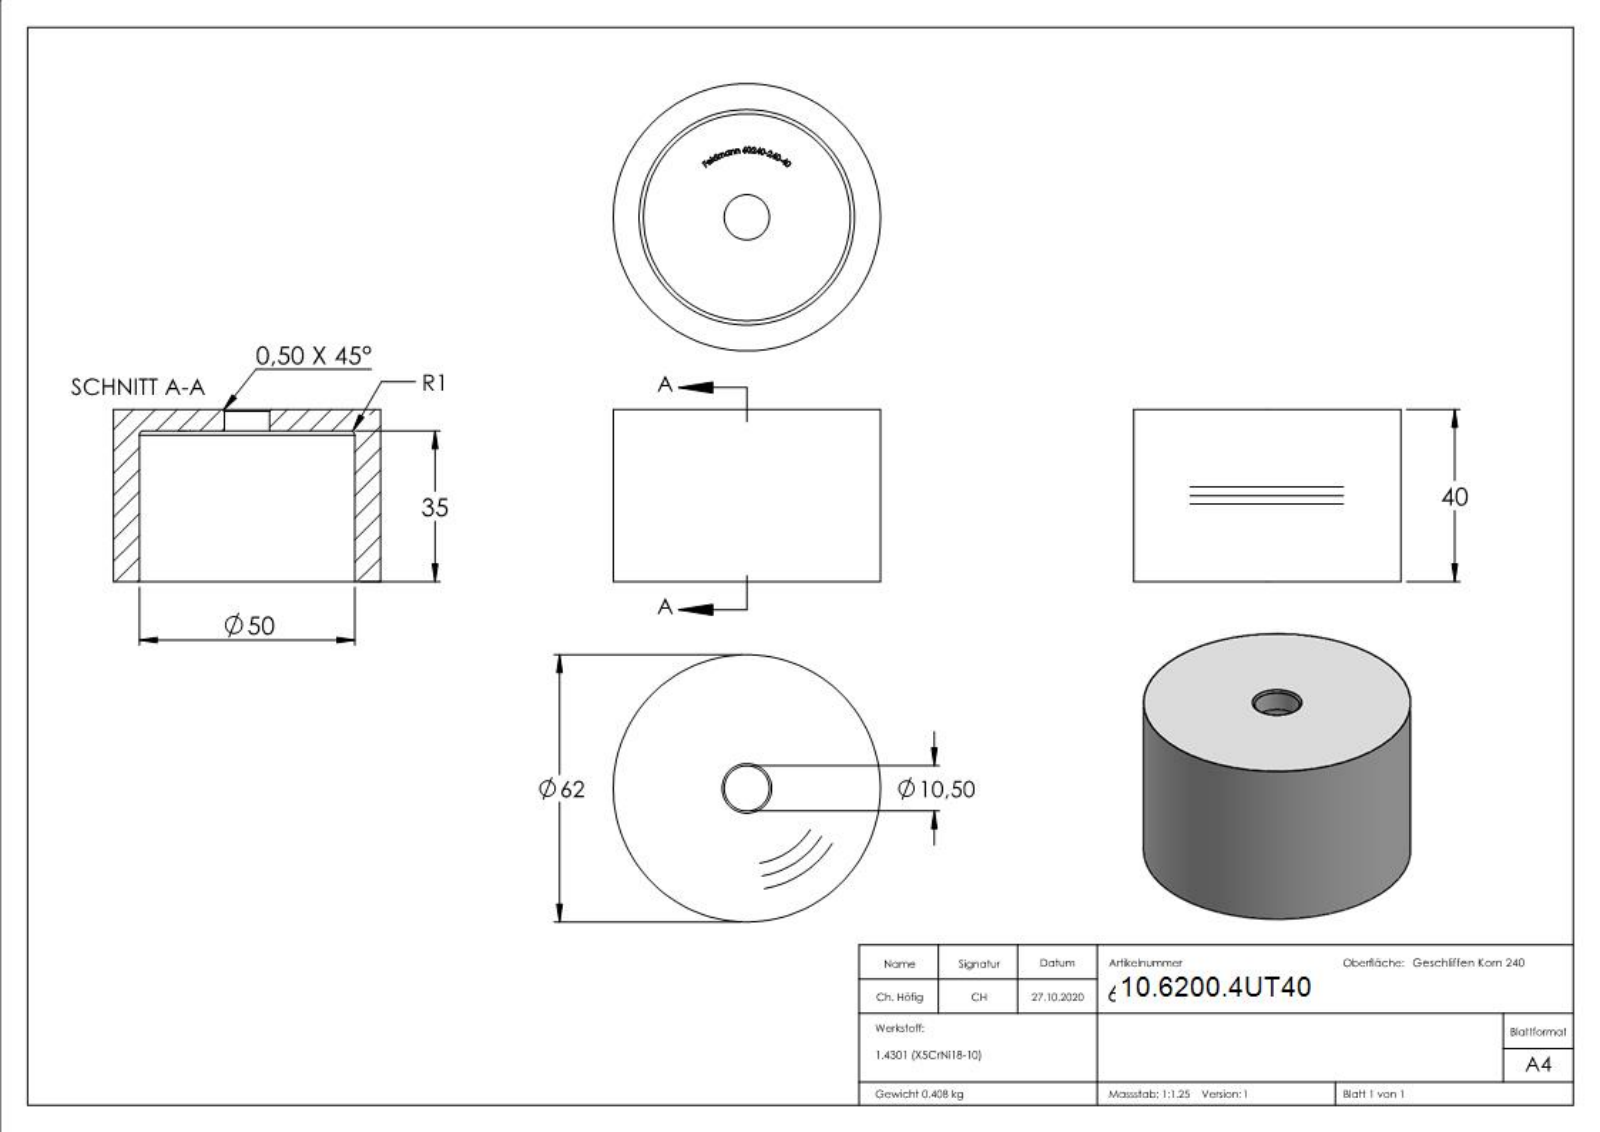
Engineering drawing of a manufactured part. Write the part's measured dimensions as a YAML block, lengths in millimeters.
part_name: "60240-240-40"
step_written_by: "SolidWorks 2018 (CONFIG_CONTROL_DESIGN)"
units: millimeters
bodies: {solids: 1, faces: 265, planar: 150, cylindrical: 6, other: 109}
overall_size: [62, 62, 40]
volume: 51636
surface_area: 19253
round_holes:
  - {diameter: 10.5, count: 1}
  - {diameter: 50, count: 1}
round_bosses_or_shafts:
  - {diameter: 62, count: 1}
face_to_face_distances: [5, 35, 40, 35.1, 4.9, 0.54, 1.33, 0.73, 1.46, 0.67]
